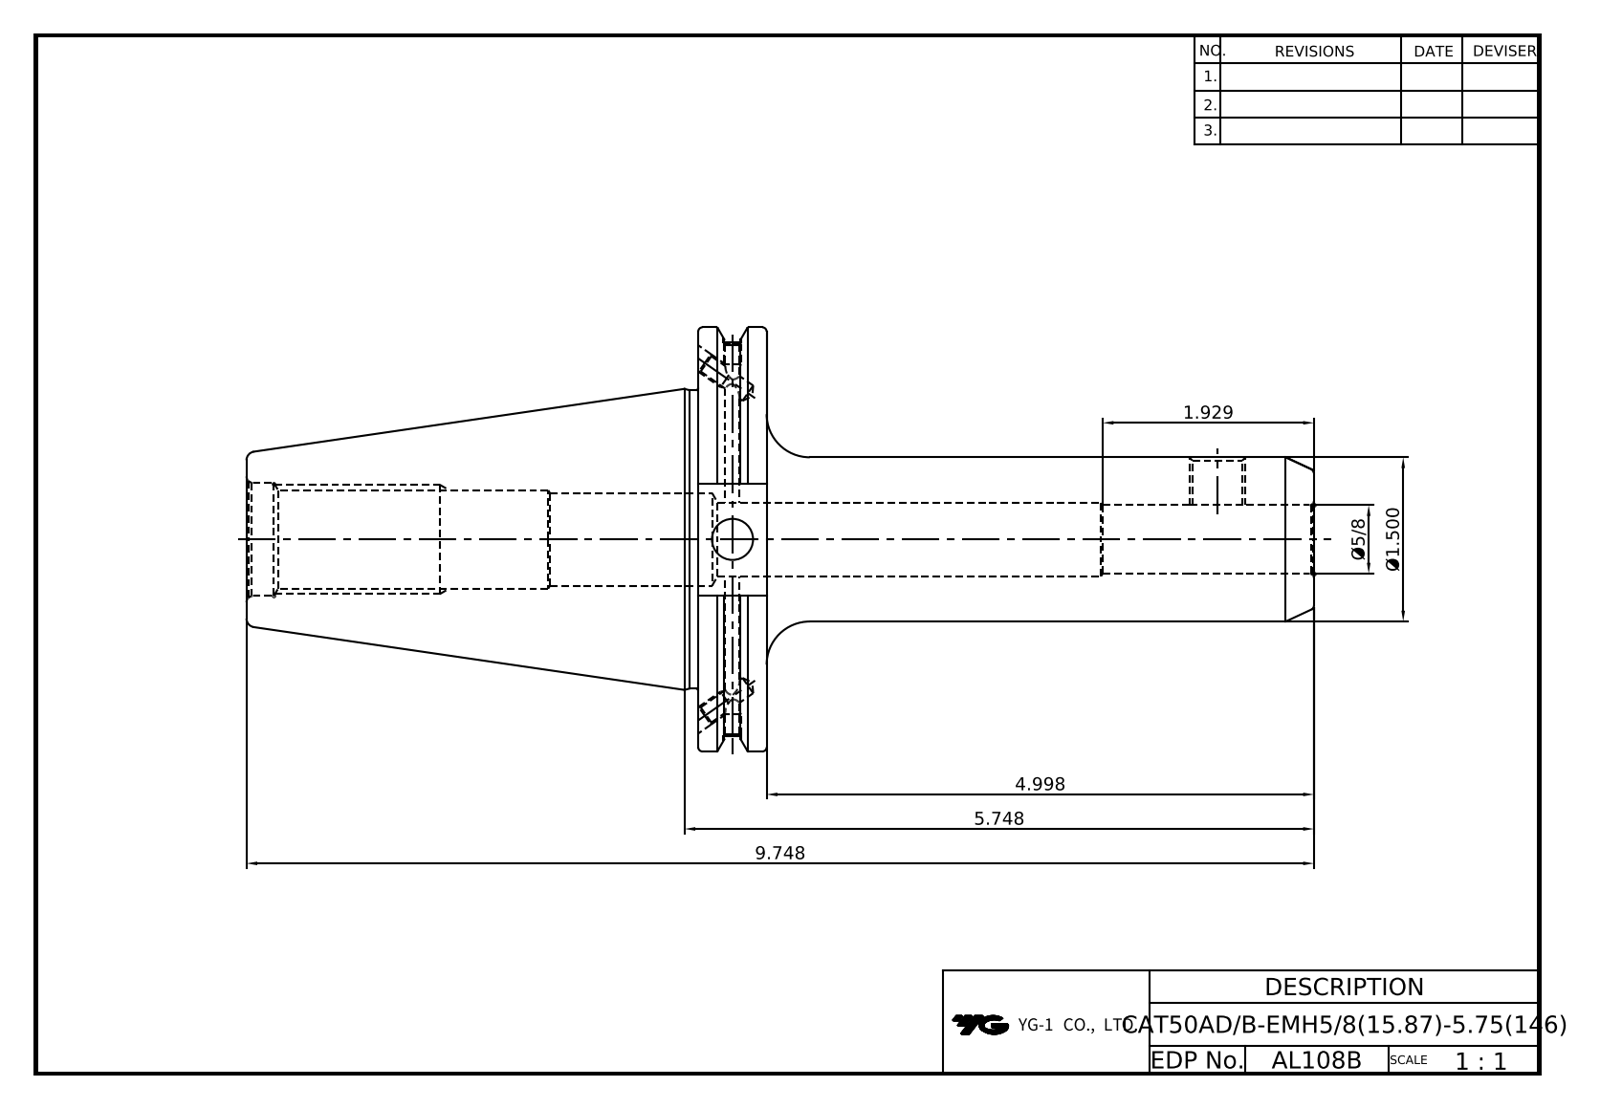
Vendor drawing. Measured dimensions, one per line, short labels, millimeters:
name: LO-CAT50ADB-EMH15.875-146
written by: Autodesk Inventor 2024 (AUTOMOTIVE_DESIGN)
unit: mm
bodies: 1 solid, 90 faces (37 planar, 27 cylindrical, 26 other)
size: 247.6 × 98.42 × 94.69
volume: 437 216 mm³; area: 66 347 mm²
holes: 2× ⌀3.24, 2× ⌀4.13, 2× ⌀4.2, 2× ⌀5, 1× ⌀9.53, 1× ⌀11.33, 1× ⌀15.88, 1× ⌀17, 1× ⌀21.5, 1× ⌀21.97, 1× ⌀26.2
bosses: 1× ⌀98.42, 1× ⌀91.29, 1× ⌀69.25, 1× ⌀38.1
face distances: 15.88, 104.77, 120.65, 247.6, 142.83, 126.95, 73.03, 25.9, 110.82, 6.05
